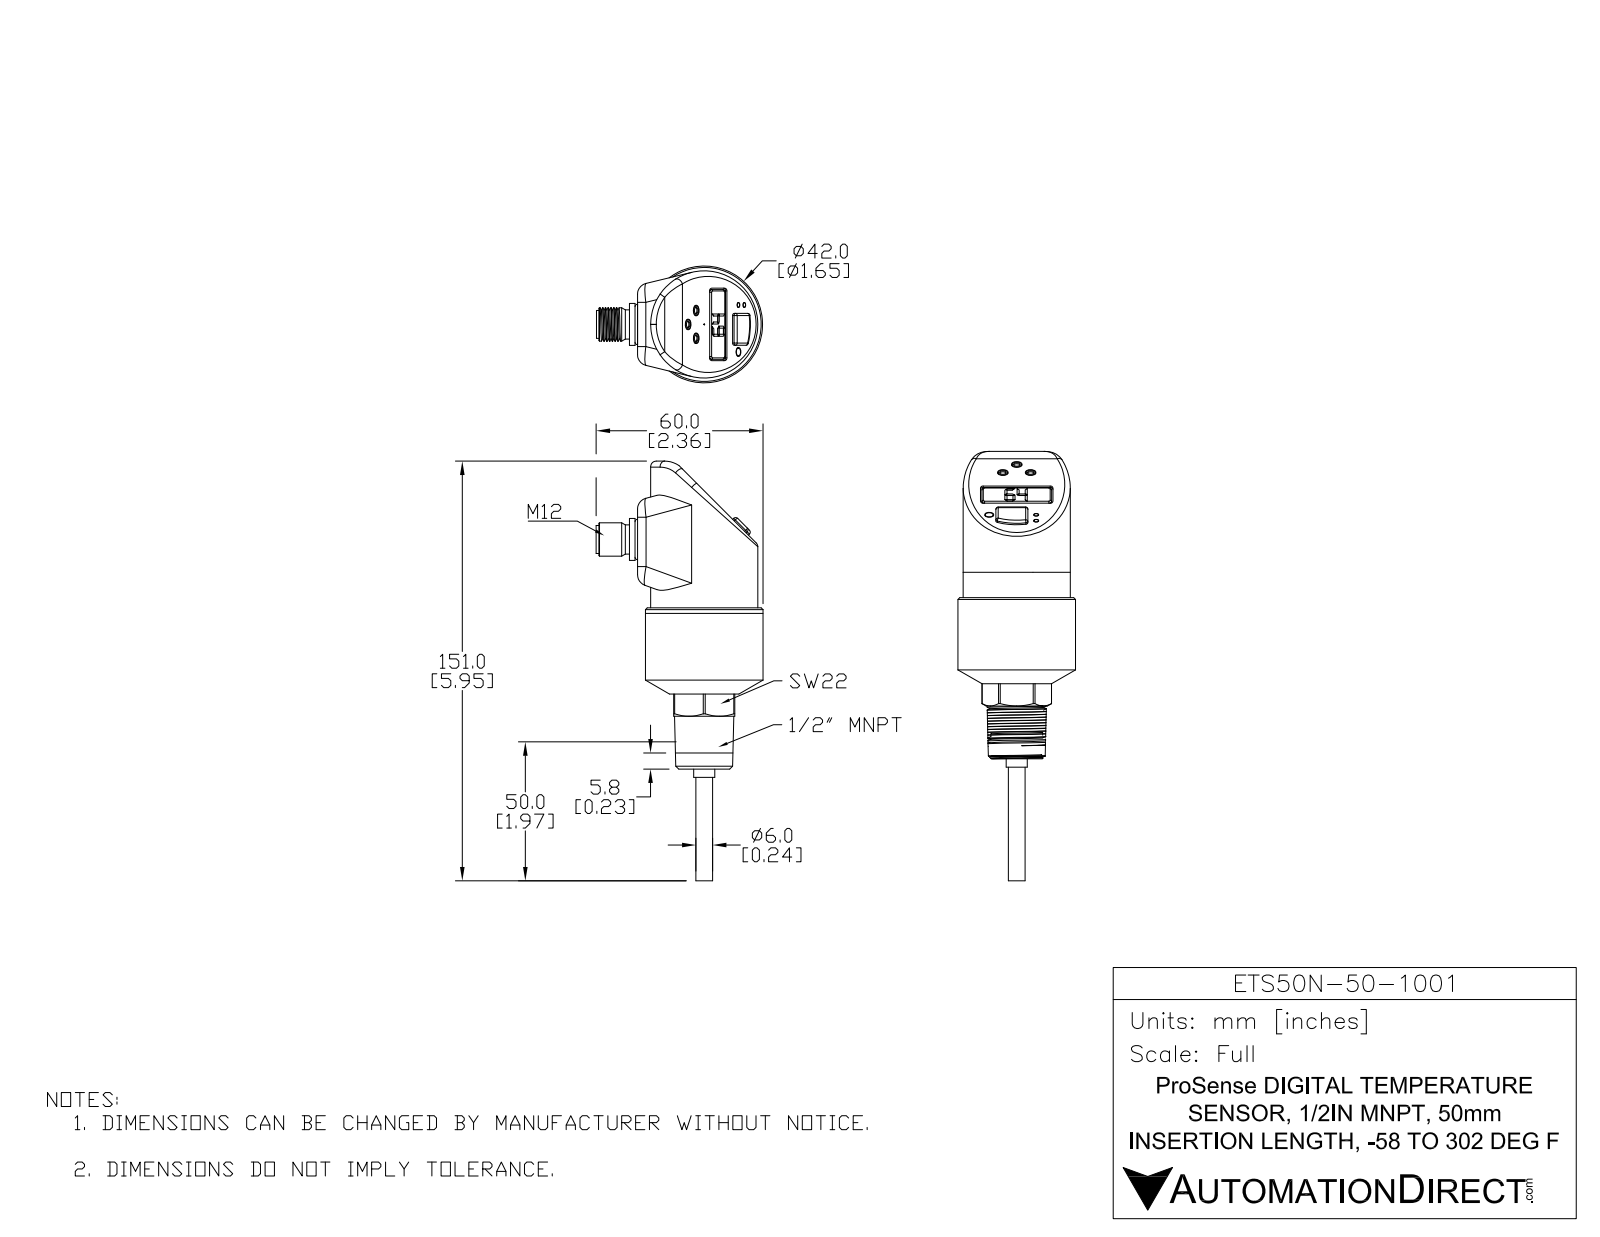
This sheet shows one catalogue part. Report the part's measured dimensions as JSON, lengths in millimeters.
{"part_name": "ETS50N-50-1001", "step_written_by": "SolidWorks 2016 (AUTOMOTIVE_DESIGN)", "units": "millimeters", "bodies": {"solids": 1, "faces": 324, "planar": 138, "cylindrical": 95, "other": 91}, "overall_size": [154.49, 59.95, 42.3], "volume_mm3": 107744, "surface_area_mm2": 18719, "round_holes": [[8.45, 1], [11, 1]], "round_bosses_or_shafts": [[1.4, 4], [1, 4], [42.3, 1], [38.55, 1], [15.1, 1], [14.56, 1], [12, 1], [10.5, 1]], "partial_cylinders_radius": [[1, 8], [0.8, 7], [0.5, 4], [3.99, 4], [7, 4], [0.61, 1], [2, 1], [9.01, 1]], "face_to_face_distances": [22, 57.99, 13.9, 13, 0.9, 2, 2.9, 15.9, 37.9, 35]}
